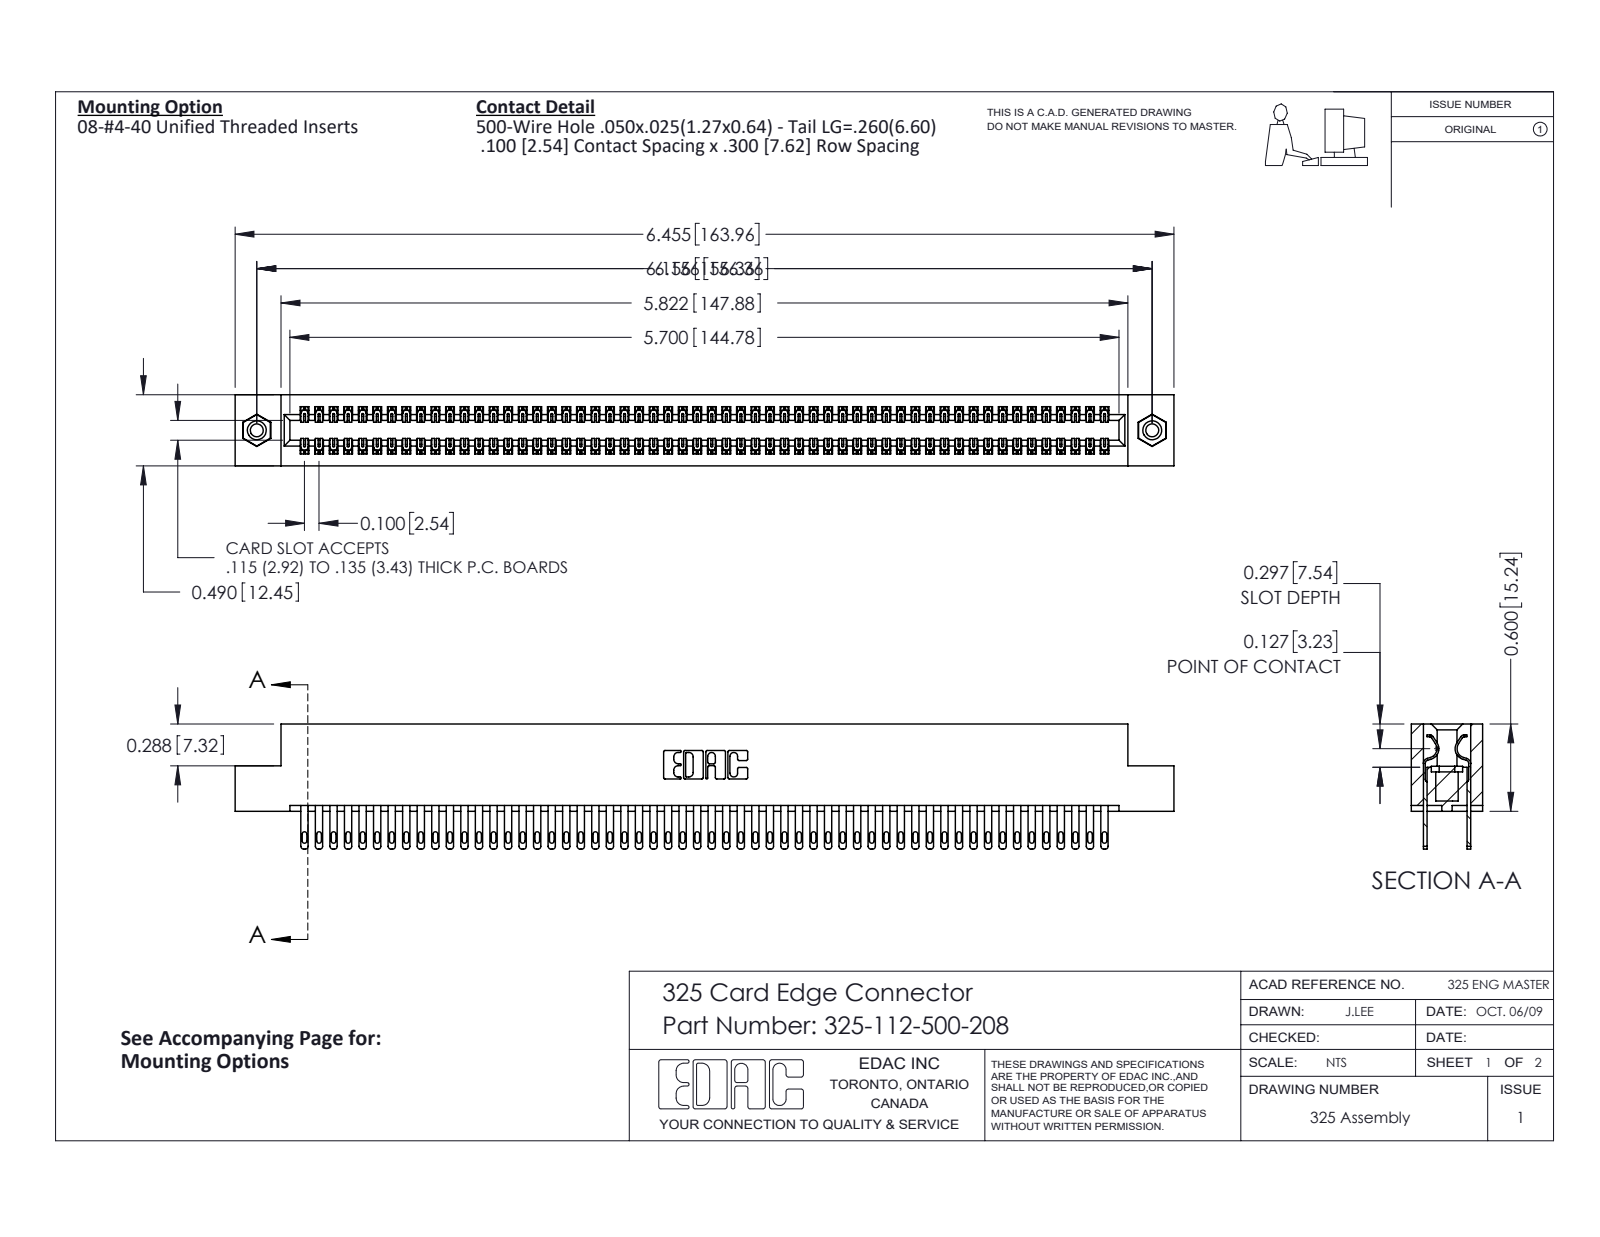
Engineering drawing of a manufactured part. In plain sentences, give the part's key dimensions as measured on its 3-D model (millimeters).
The part is named "345-250-001_345-250-003-102; 325-292-001_325-293-100; 325 Part_TI; 325-112-500-208". Its 3-D file was written by "SolidWorks 2016 (CONFIG_CONTROL_DESIGN)". It is 115 solids with 5550 faces: 3462 planar, 2072 cylindrical and 16 other. Overall it measures 164 by 21.8 by 12.4 millimeters. Its volume is 21 630 cubic millimeters and its surface area 27 700 square millimeters. Round holes: 2 of diameter 2.3, 2 of diameter 3.2, 2 of diameter 4.1. Round bosses or shafts: 2 of diameter 3.9. Partial cylindrical surfaces (rounded edges, fillets, slot ends): 168 of radius 0.2, 112 of radius 0.4, 112 of radius 0.5, 22 of radius 0.3, 6 of radius 0.2, 6 of radius 0.8, 3 of radius 0.7, 2 of radius 0.4. The main face-to-face distances are 2.1, 10.3, 7.6, 2.7, 9.7, 0.6, 12.4, 8.3, 7, 6.7. The hole center spacings are 156.4.
